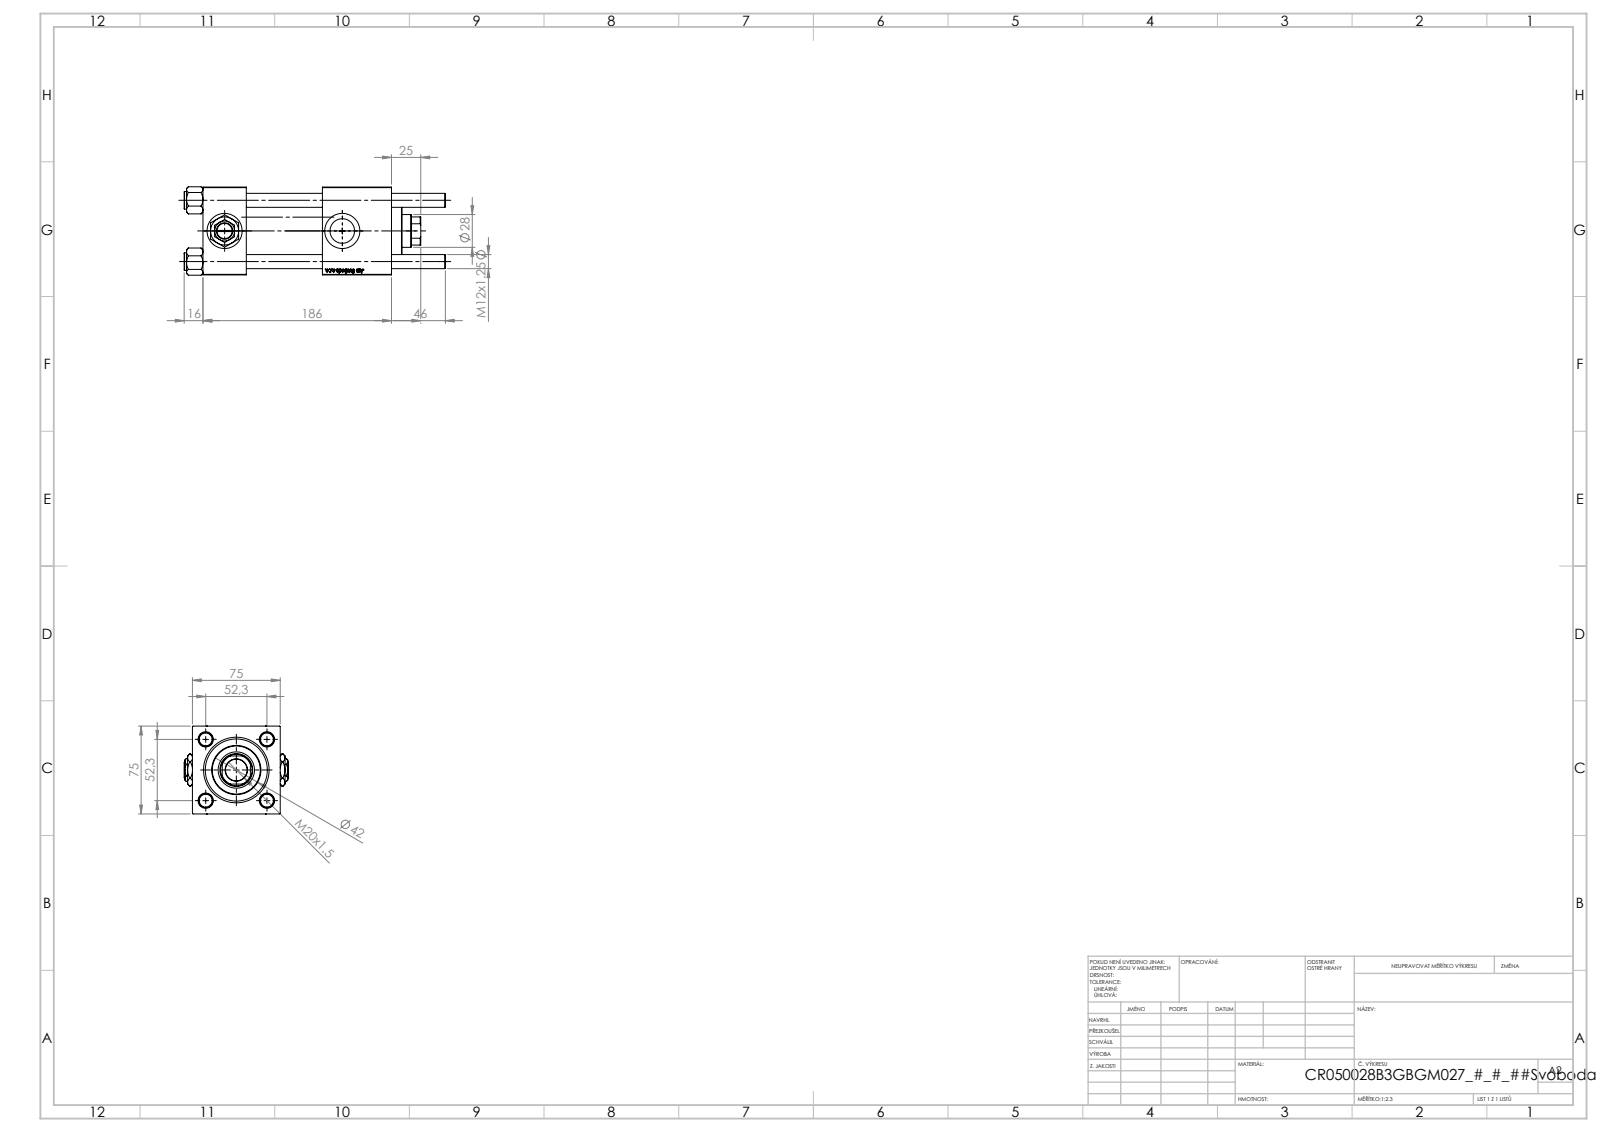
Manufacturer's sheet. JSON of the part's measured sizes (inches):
{"part_name": "NUT_M5_B; V215CR_B_TYCINKA; V215CR_VCP_B; V215_VC_A (+2 more)", "step_written_by": "SolidWorks 2019 (CONFIG_CONTROL_DESIGN)", "units": "inches", "bodies": {"solids": 13, "faces": 1257, "planar": 479, "cylindrical": 88, "other": 690}, "overall_size": [8.78, 3.504, 2.97], "volume_in3": 43.21, "surface_area_in2": 272.2, "round_holes": [[0.472, 4], [0.276, 2], [0.825, 2], [1.181, 2], [0.728, 1], [1.102, 1], [1.22, 1], [1.614, 1], [1.969, 1], [2.087, 1]], "round_bosses_or_shafts": [[0.591, 4], [2.205, 1], [1.654, 1]], "partial_cylinders_radius": [[0.531, 1]], "face_to_face_distances": [2.953, 1.457, 6.339, 4.882, 4.016, 2.559, 2.323, 5.209, 3.752, 1.193], "hole_center_spacings": [1.456, 2.059, 2.912, 3.957]}
